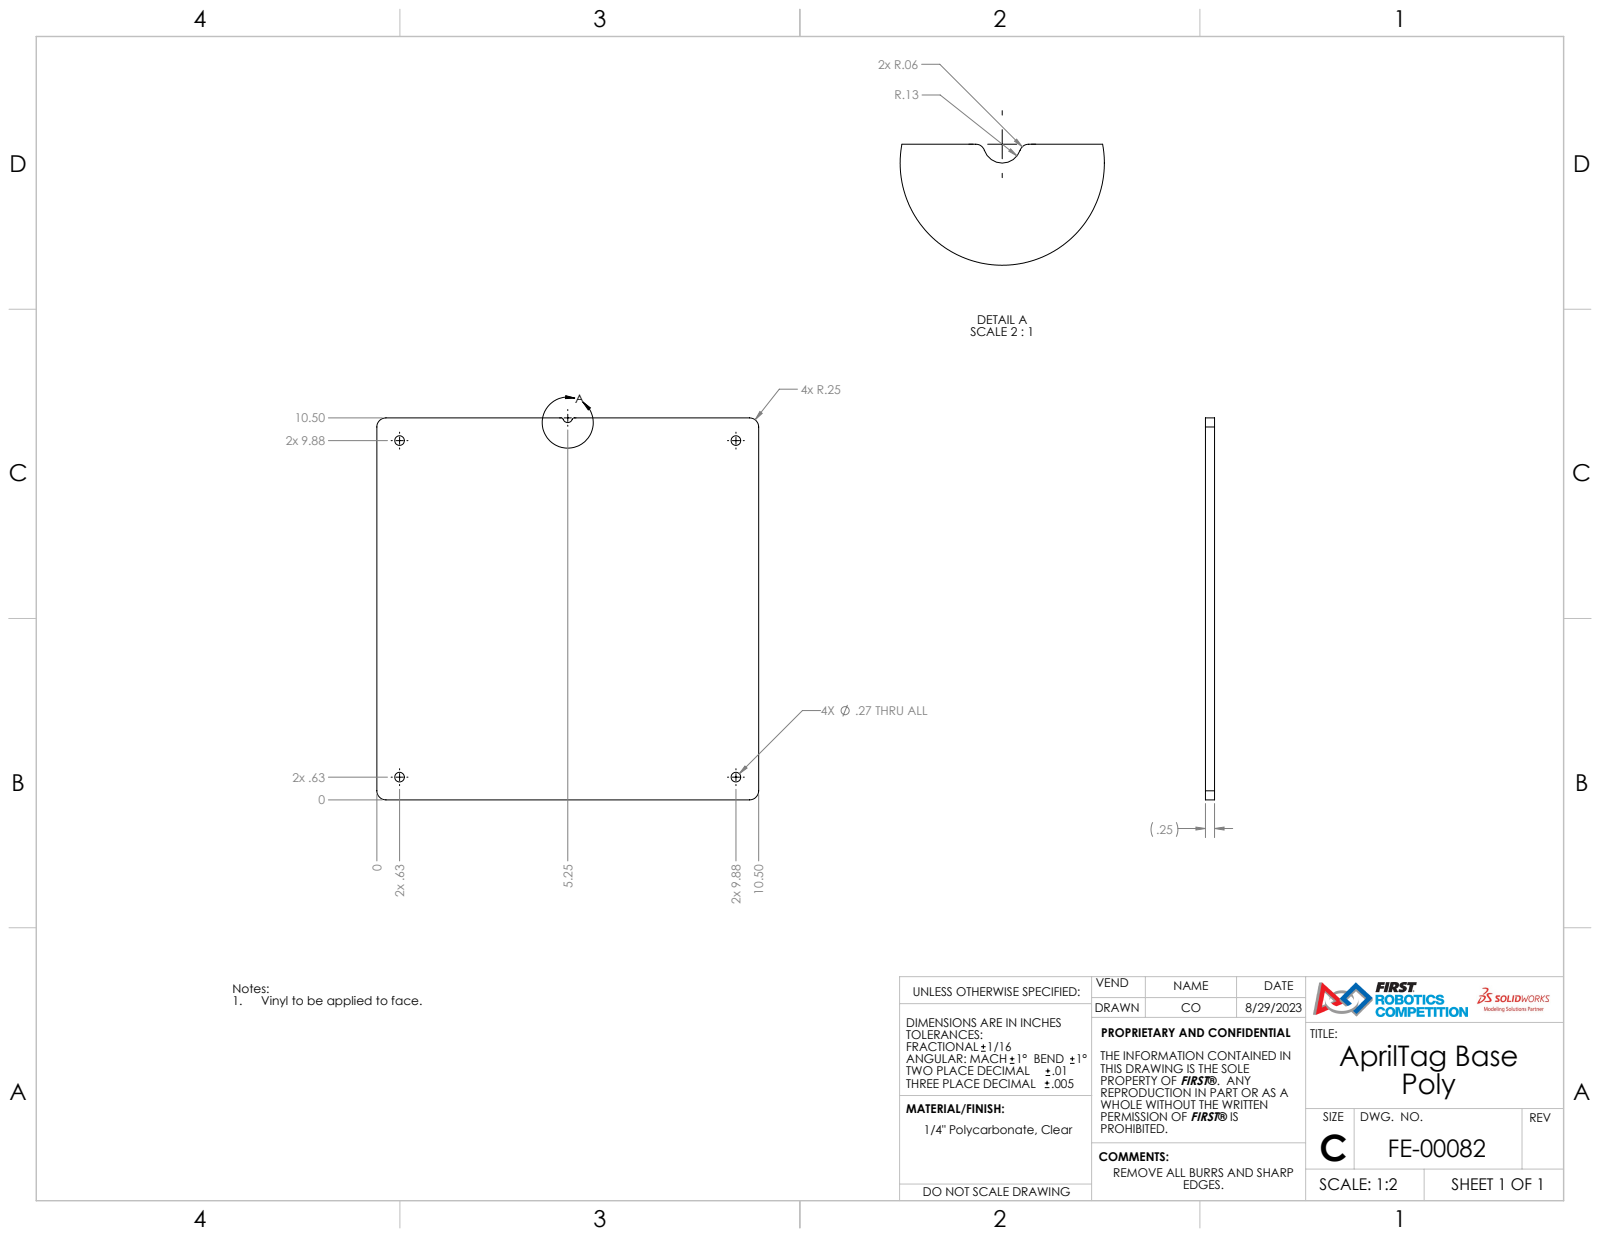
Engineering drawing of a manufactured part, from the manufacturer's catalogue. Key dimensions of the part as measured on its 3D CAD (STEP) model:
Part name (STEP PRODUCT): am-5187_pc April Tag Base Plate FE-00082
STEP written by: SolidWorks 2024 (CONFIG_CONTROL_DESIGN)
Units: inches
Bodies: 1 solid, 22 faces (7 planar, 15 cylindrical, 0 other)
Overall size (bounding box): 10.5 × 10.5 × 0.25
Volume: 27.49 in³ · Surface area: 231.1 in²
Round holes (diameter × count): ⌀0.266 ×4
Partial cylindrical surfaces — rounded edges, fillets, slot ends (radius × count): R0.25 ×4, R0.062 ×1, R0.063 ×1, R0.13 ×1
Main face-to-face distances: 0.25, 10.5
Hole centre spacings: 9.25, 9.25, 9.25, 13.081, 13.082
